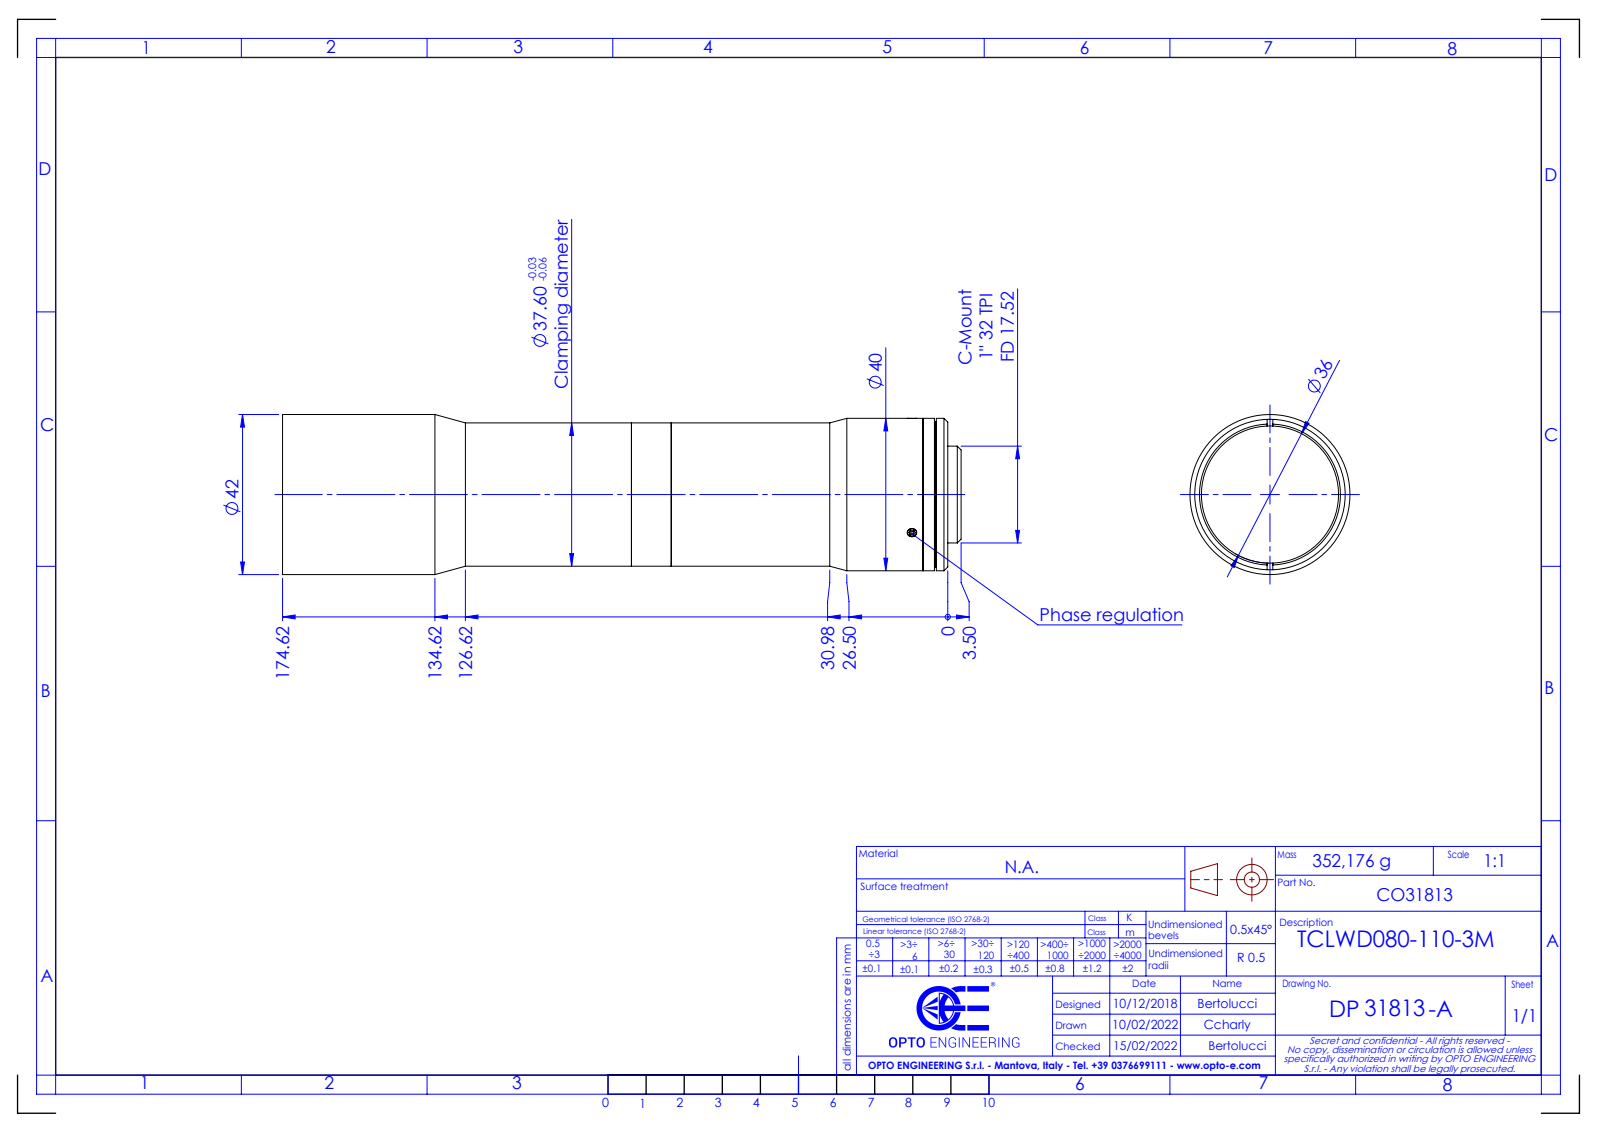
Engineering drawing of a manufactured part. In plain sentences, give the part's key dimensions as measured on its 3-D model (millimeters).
The part is named "DP31813-A_TCLWD080-110-3M". Its 3-D file was written by "SolidWorks 2021 (CONFIG_CONTROL_DESIGN)". It is 0 solids with 83 faces: 38 planar, 26 cylindrical and 19 other. Overall it measures 178.12 by 42 by 42 millimeters. Round holes: 1 of diameter 22.5, 1 of diameter 25.5, 1 of diameter 32, 1 of diameter 36, 1 of diameter 39.5. Round bosses or shafts: 1 of diameter 42, 1 of diameter 40, 1 of diameter 37.6, 1 of diameter 25.4. The main face-to-face distances are 3.5, 3, 0.5, 69.03, 69.53, 72.53, 6.5, 66.03, 101.88, 167.91.
